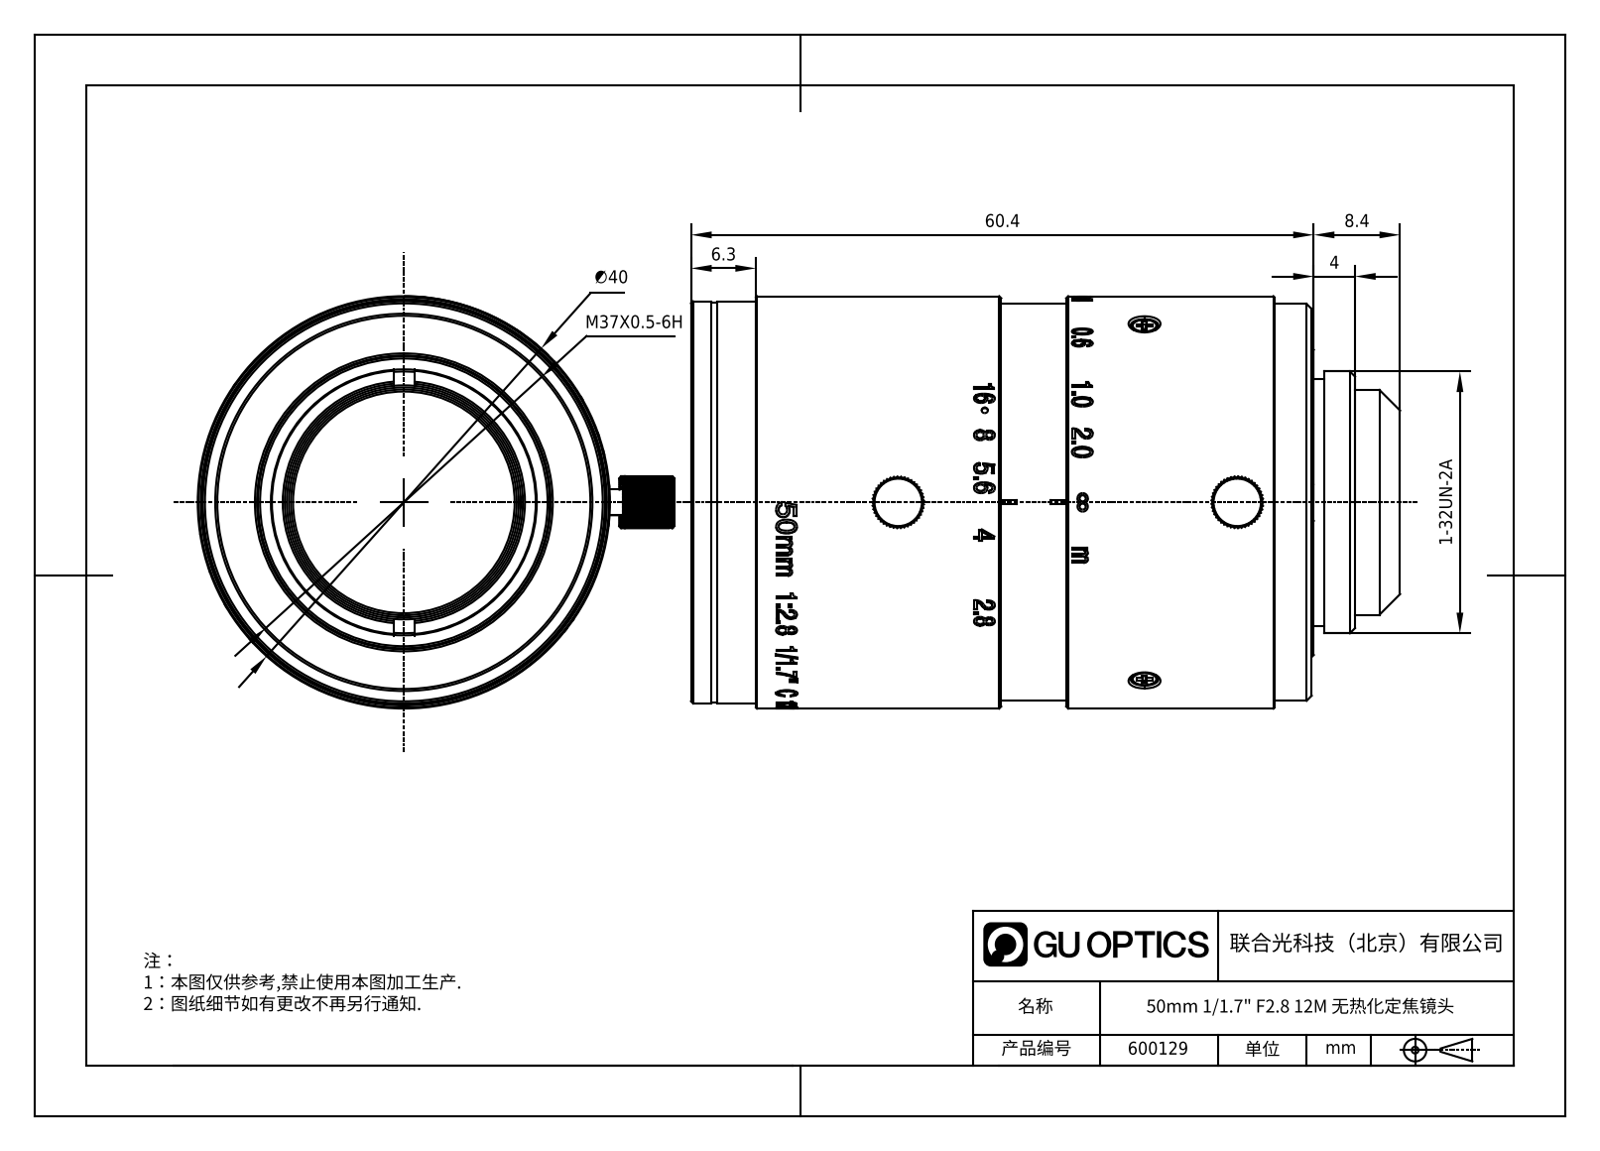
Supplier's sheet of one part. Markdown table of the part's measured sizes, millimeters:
| quantity | value |
| --- | --- |
| part name | I741411C-615_1_1.stp; DZO_LA5028A_1806-4_ASM_1_ASM_1_ASM.stp; MANIFOLD_SOLID_BREP_1985_1_1.stp; 600129.stp (+8 more) |
| STEP written by | SolidWorks 2020 (CONFIG_CONTROL_DESIGN) |
| units | millimeters |
| bodies | 26 solids, 2605 faces (724 planar, 630 cylindrical, 1251 other) |
| overall size | 68.8 × 46.25 × 40 |
| volume | 39 292 mm³ |
| surface area | 43 884 mm² |
| round holes (diameter × count) | 2 × 6, 2.7 × 6, 1 × 5, 3.2 × 4, 1.3 × 3, 1.5 × 3, 1.8 × 3, 1.2 × 2, 1.6 × 1, 9.3 × 1, 10.5 × 1, 13 × 1 |
| round bosses / shafts (diameter × count) | 2.5 × 8, 1.4 × 7, 2.8 × 3, 1.7 × 3, 2 × 2, 0.6 × 2, 40 × 1, 39 × 1 |
| partial cylindrical surfaces (radius × count) | 0.13 × 22, 0.3 × 18, 0.75 × 6, 1.35 × 6, 2 × 6, 2.45 × 6, 2.65 × 6, 0.74 × 3 |
| main face-to-face distances | 2.63, 50.63, 3, 2.53, 48.1, 50.73, 34.23, 4, 52.1, 54.63 |
| hole center spacings | 8.15, 9, 14.5, 15.75, 23.9, 24.75, 25.12, 32.9 |
